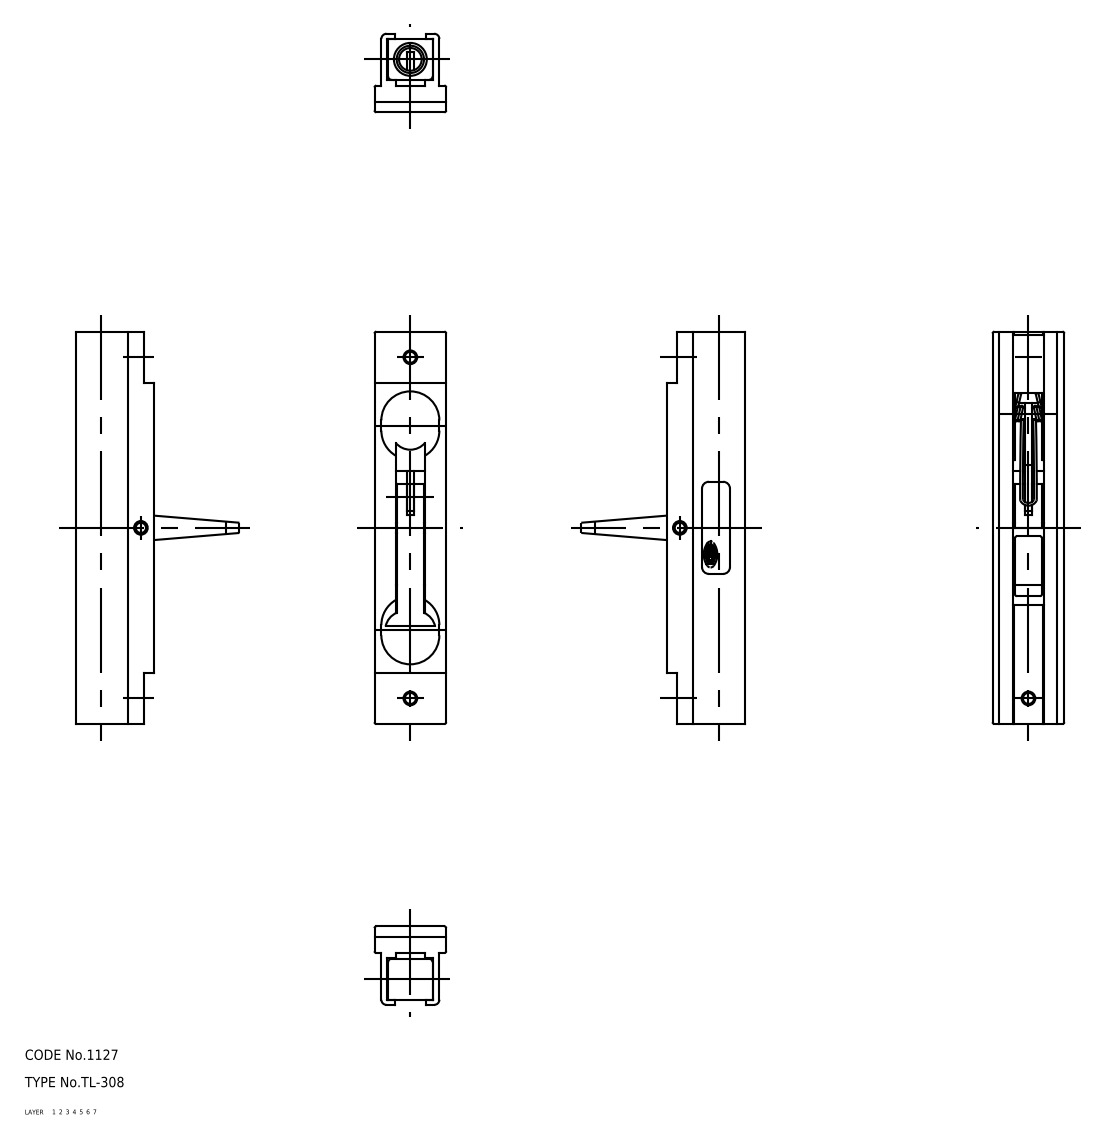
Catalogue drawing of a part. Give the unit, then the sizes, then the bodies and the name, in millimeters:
Units: millimetres
Overall size (bounding box): 115 × 23.1 × 21
Volume: 27 718 mm³ · Surface area: 23 679 mm²
Bodies: 7 solids, 206 faces (0 planar, 0 cylindrical, 206 other)
Part name (STEP PRODUCT): pin_B; lever; spring; pin_A (+4 more)
STEP written by: CADfix (AUTOMOTIVE_DESIGN)
